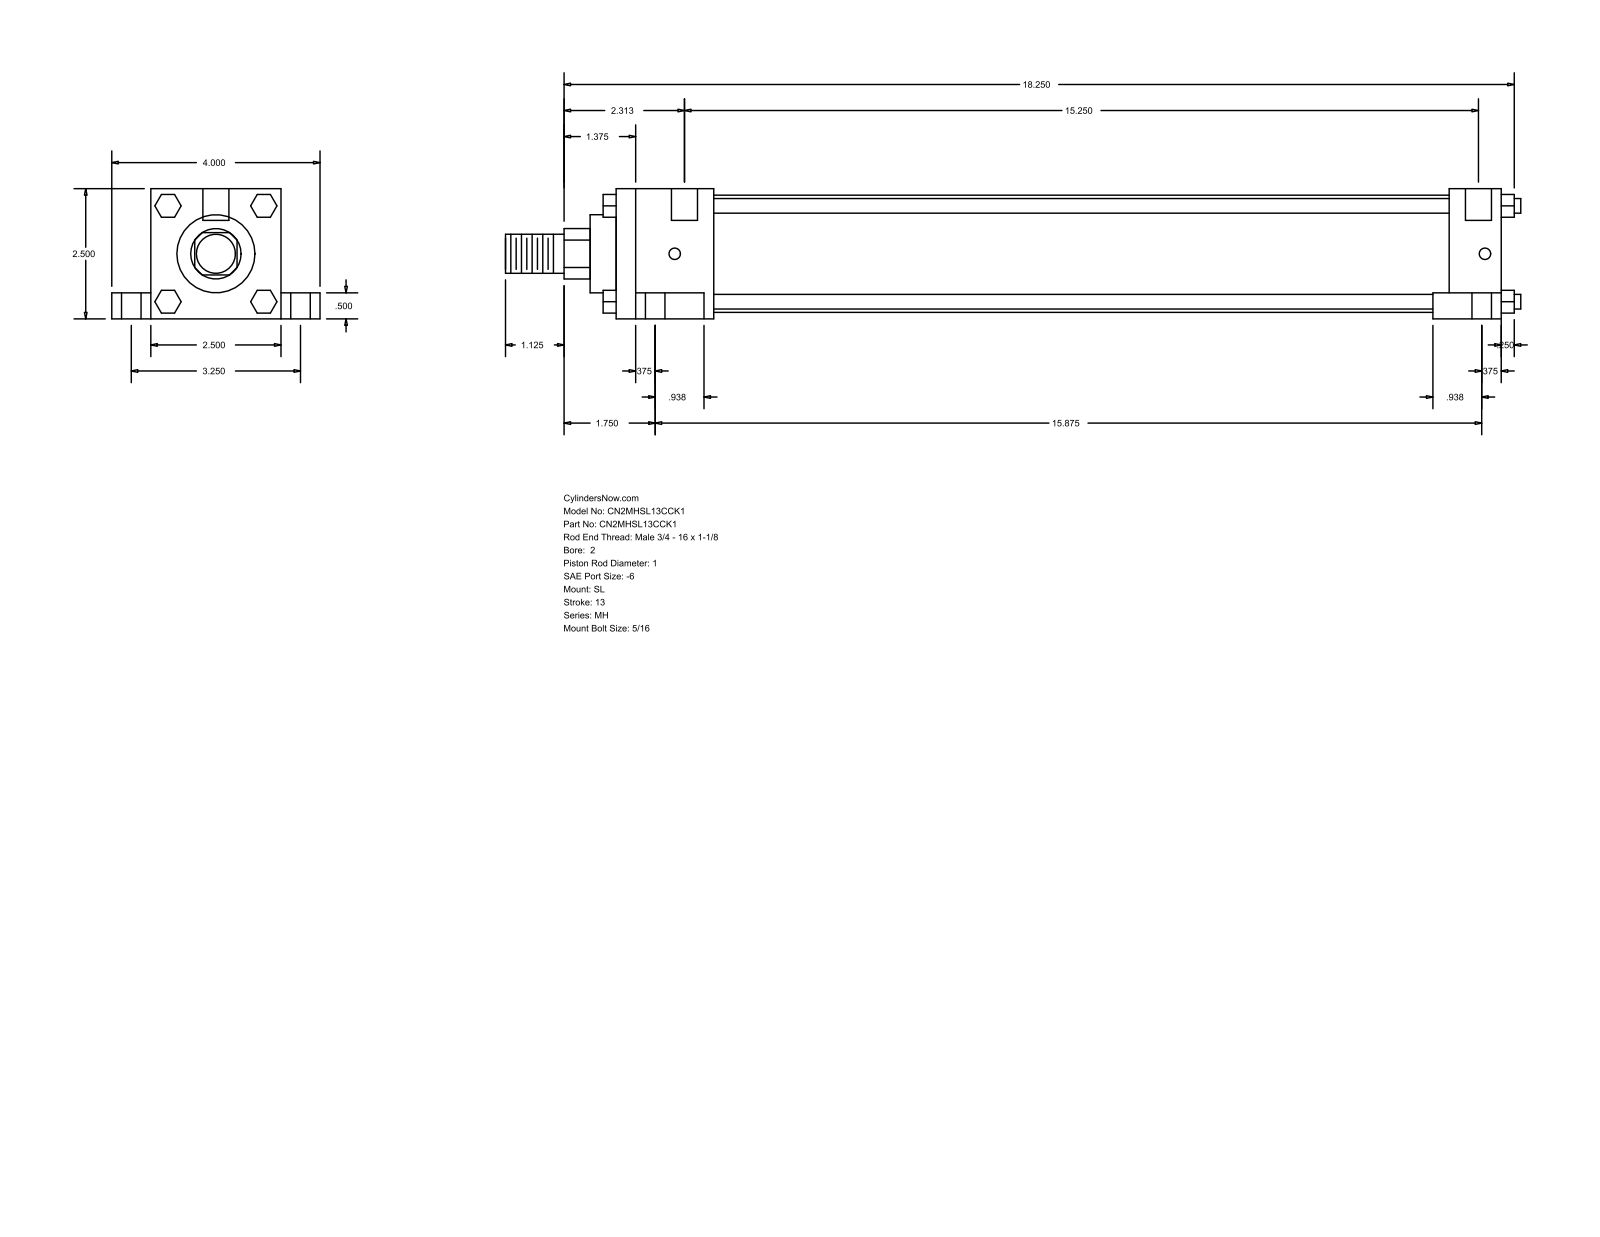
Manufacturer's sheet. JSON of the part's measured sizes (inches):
{"part_name": "MH_SL__0200_1", "step_written_by": "GSSL Pune (CONFIG_CONTROL_DESIGN)", "units": "inches", "bodies": {"solids": 0, "faces": 148, "planar": 112, "cylindrical": 36, "other": 0}, "overall_size": [19.5, 4, 2.5], "round_holes": [[0.219, 4], [0.375, 4], [0.625, 4], [0.5, 2]], "round_bosses_or_shafts": [[0.281, 4], [2.25, 1], [1.5, 1], [1, 1], [0.75, 1]], "partial_cylinders_radius": [[0.484, 1]], "face_to_face_distances": [2.5, 17, 0.5, 0.75, 2, 3.25, 1, 16, 1.875, 14.125], "hole_center_spacings": [1.626, 1.668, 1.719, 3.25, 15.398, 15.562, 15.585, 15.875]}
